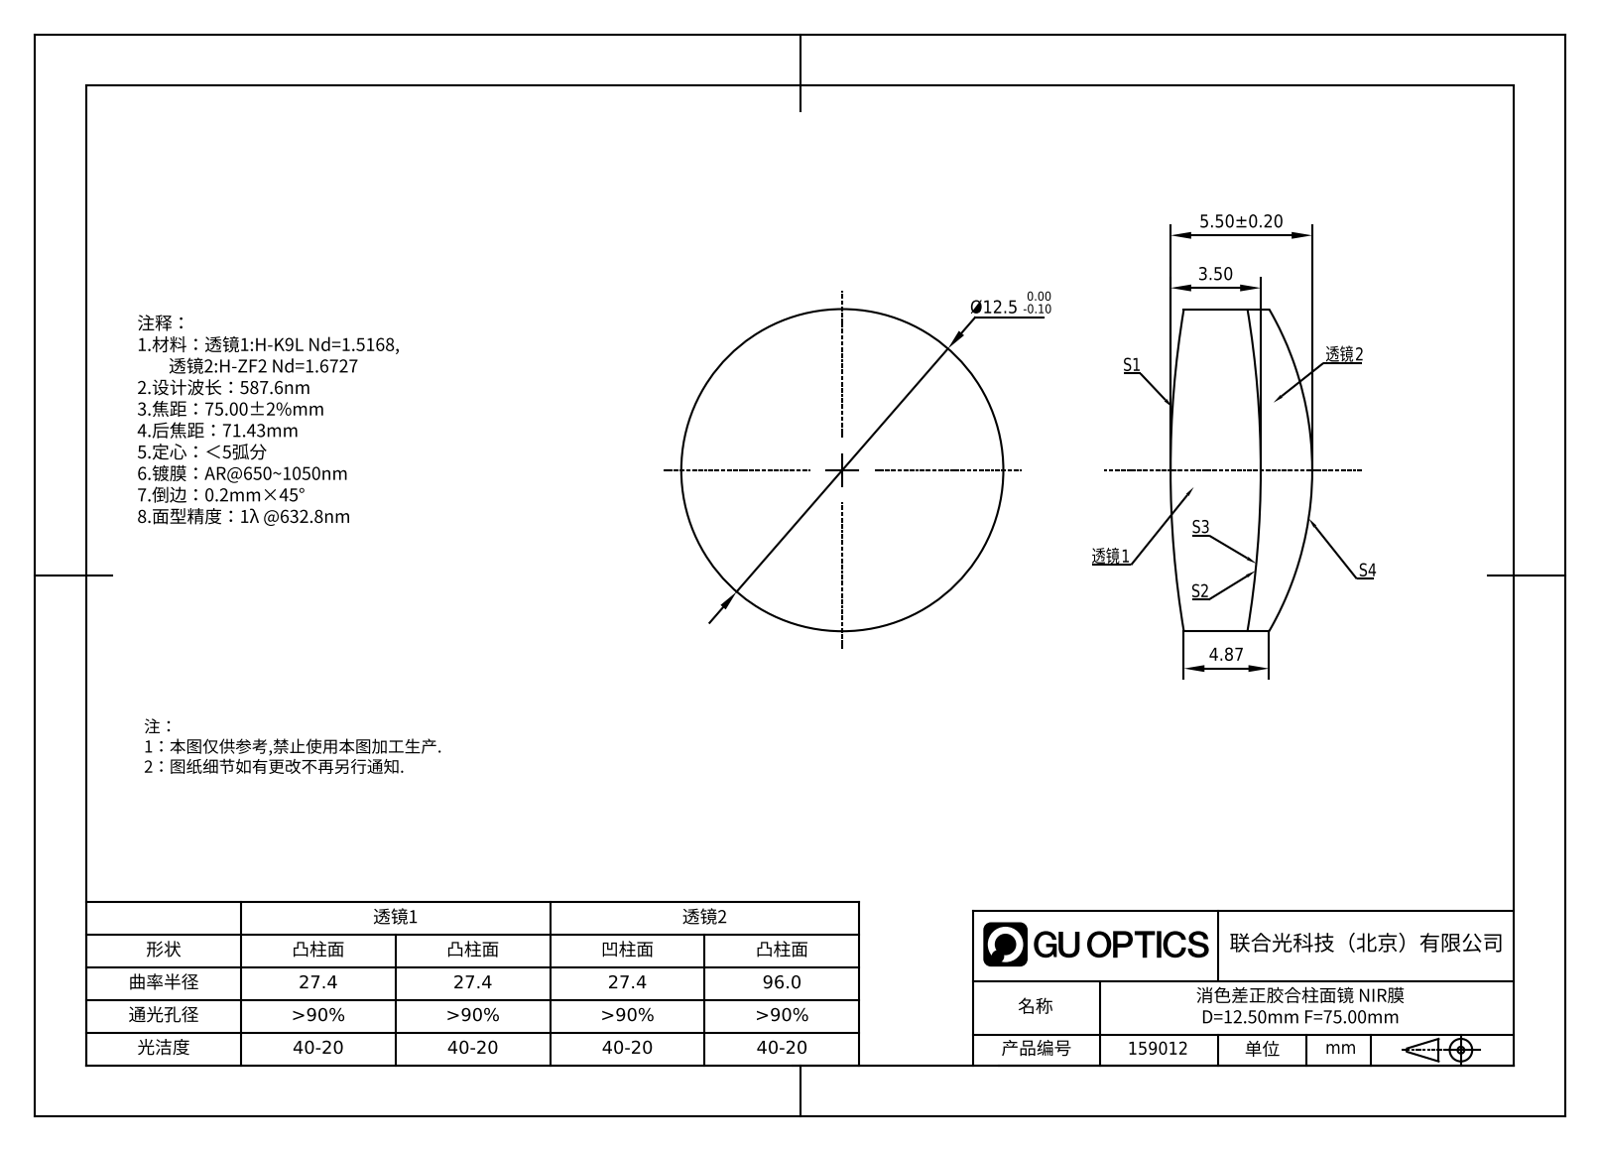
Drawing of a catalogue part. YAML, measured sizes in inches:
part_name: "159012"
step_written_by: "SolidWorks 2020 (CONFIG_CONTROL_DESIGN)"
units: inches
bodies: {solids: 1, faces: 5, planar: 0, cylindrical: 5, other: 0}
overall_size: [0.492, 0.492, 0.217]
volume: 0.037
surface_area: 0.657
round_bosses_or_shafts:
  - {diameter: 0.492, count: 1}
partial_cylinders:
  - {radius: 0.492, count: 1}
  - {radius: 1.5, count: 1}
